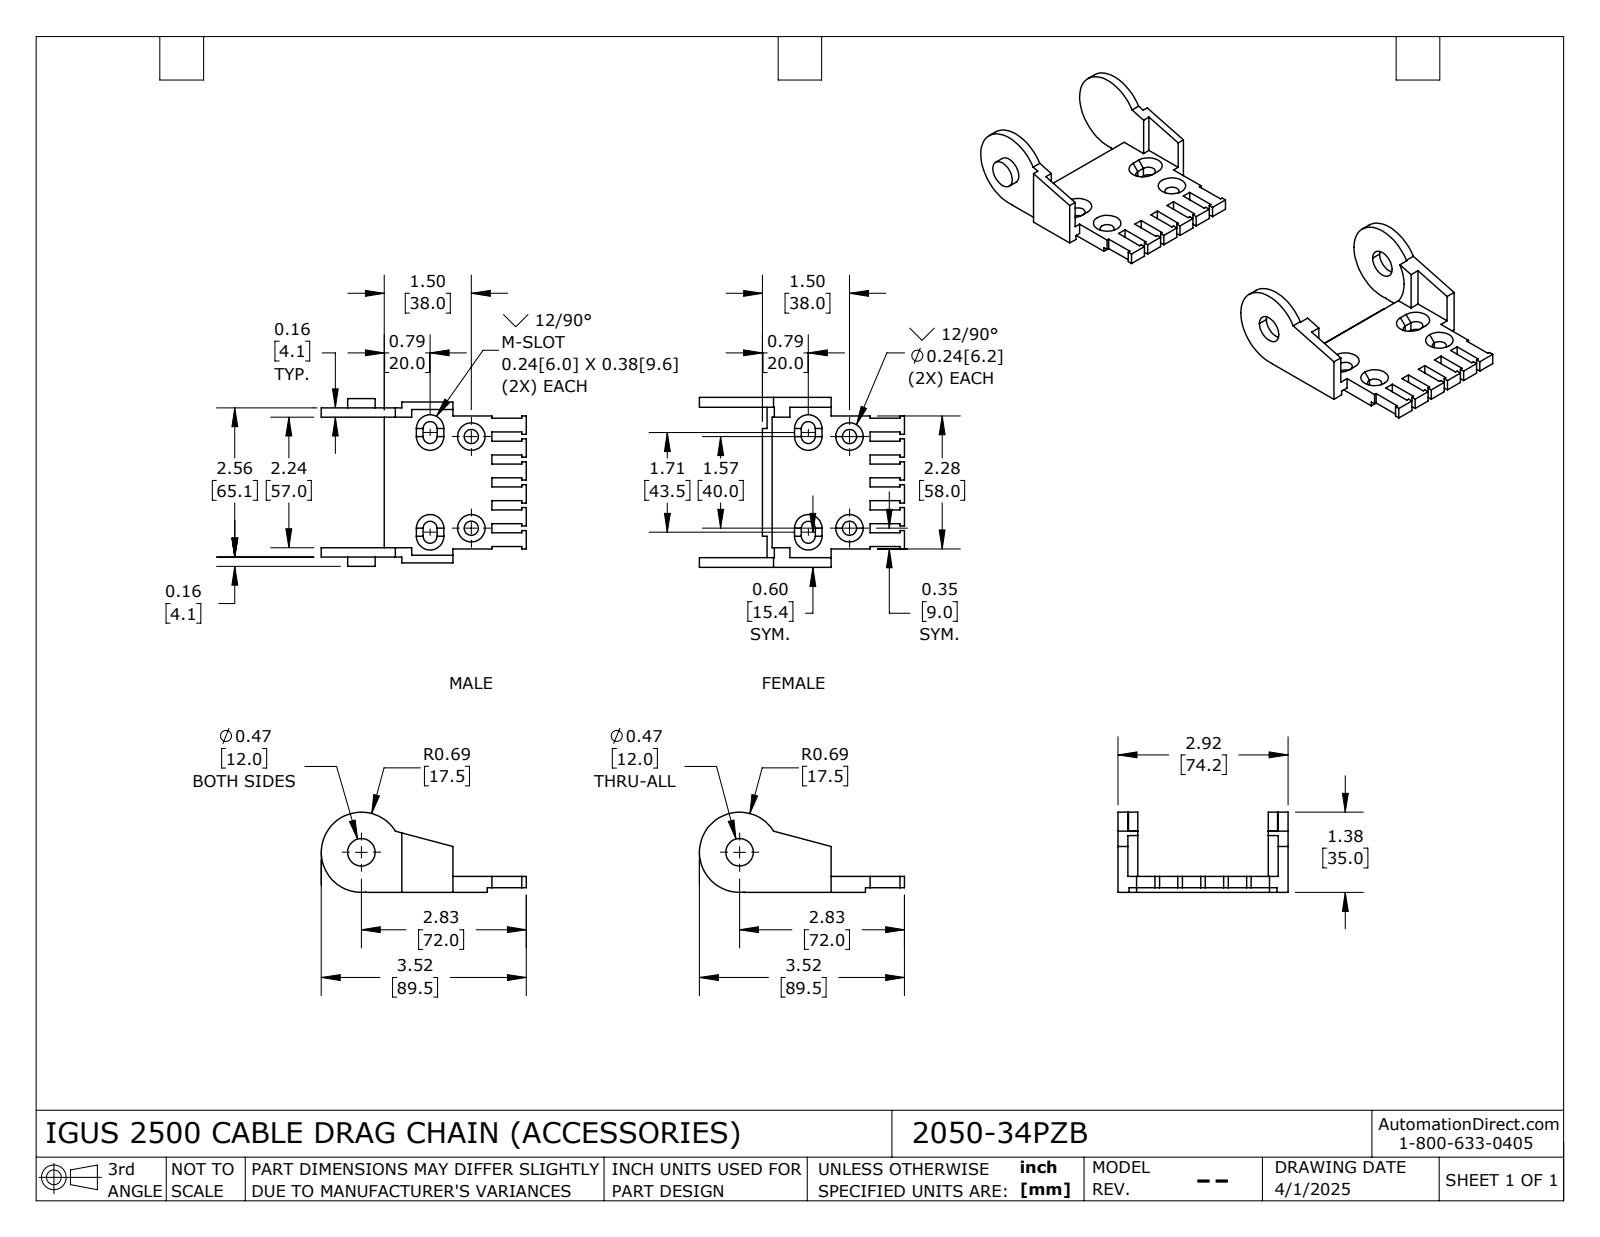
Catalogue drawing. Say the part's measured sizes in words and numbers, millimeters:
The part is named "2050-34PZB". Its 3-D file was written by "SolidWorks 2024 (AUTOMOTIVE_DESIGN)". It is 2 solids with 227 faces: 184 planar, 29 cylindrical and 14 other. Overall it measures 254.6 by 74.2 by 35 millimeters. Its volume is 67 889 cubic millimeters and its surface area 34 309 square millimeters. Round holes: 4 of diameter 6.2, 1 of diameter 12. Round bosses or shafts: 1 of diameter 12. Partial cylindrical surfaces (rounded edges, fillets, slot ends): 8 of radius 3.05, 2 of radius 17.5, 1 of radius 17.7. The main face-to-face distances are 7, 4.3, 65.6, 2, 8.6, 69.9, 61.3, 4.55, 69.65, 65.35. The hole center spacings are 40, 165.1, 169.88.
